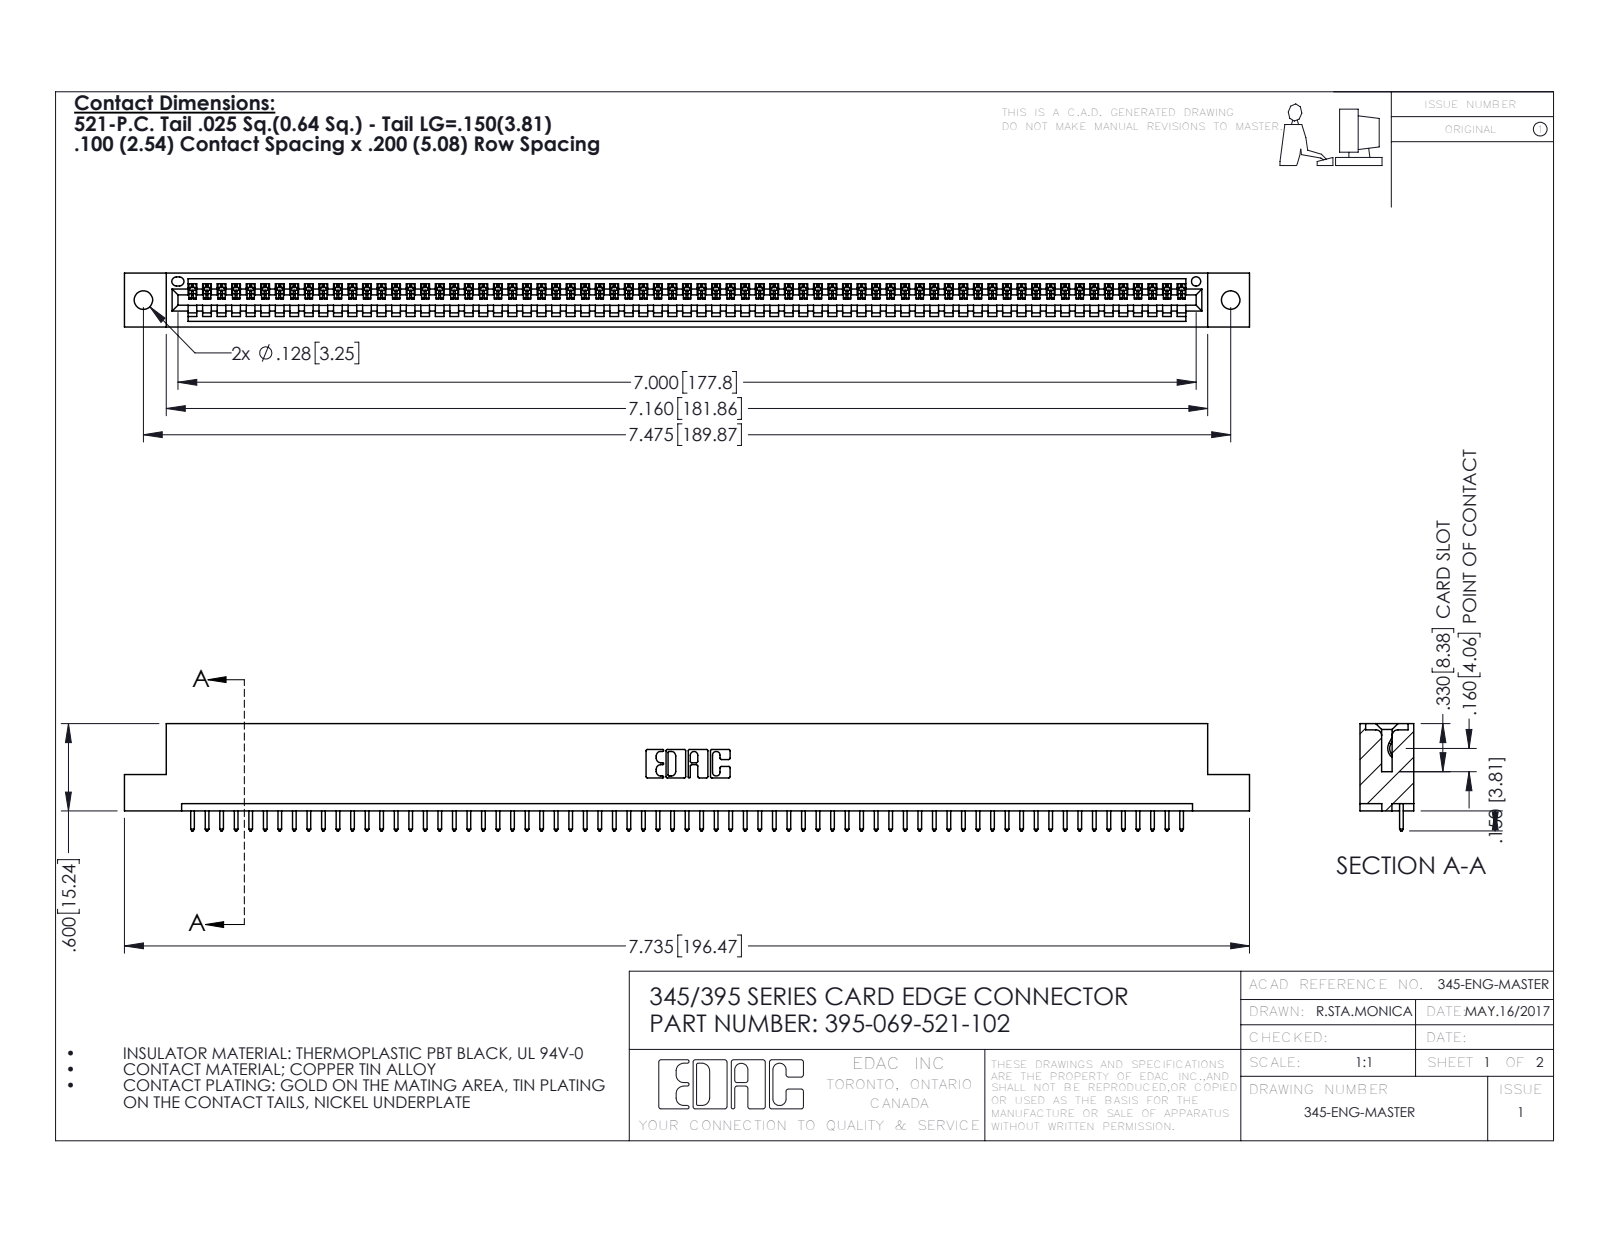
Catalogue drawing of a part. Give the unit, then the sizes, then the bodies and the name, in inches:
Units: inches
Overall size (bounding box): 7.735 × 0.737 × 0.37
Round holes (diameter × count): ⌀0.128 ×2, ⌀0.064 ×1
Partial cylindrical surfaces — rounded edges, fillets, slot ends (radius × count): R0.006 ×138, R0.01 ×138, R0.01 ×22, R0.007 ×6, R0.031 ×6, R0.026 ×3, R0.031 ×2, R0.04 ×2
Main face-to-face distances: 0.298, 0.072, 0.37, 0.2, 0.098, 0.272, 0.025, 0.225, 0.149, 0.072
Hole centre spacings: 0.27, 7.239, 7.475
Volume: 1.138 in³ · Surface area: 37.37 in²
Bodies: 70 solids, 4128 faces (2840 planar, 1288 cylindrical, 0 other)
Part name (STEP PRODUCT): 345-292-001_345-293-121; 395-069-521-102; 345 Part_Flush Mounting Lugs - 0.128 Dia
STEP written by: SolidWorks 2016 (CONFIG_CONTROL_DESIGN)
